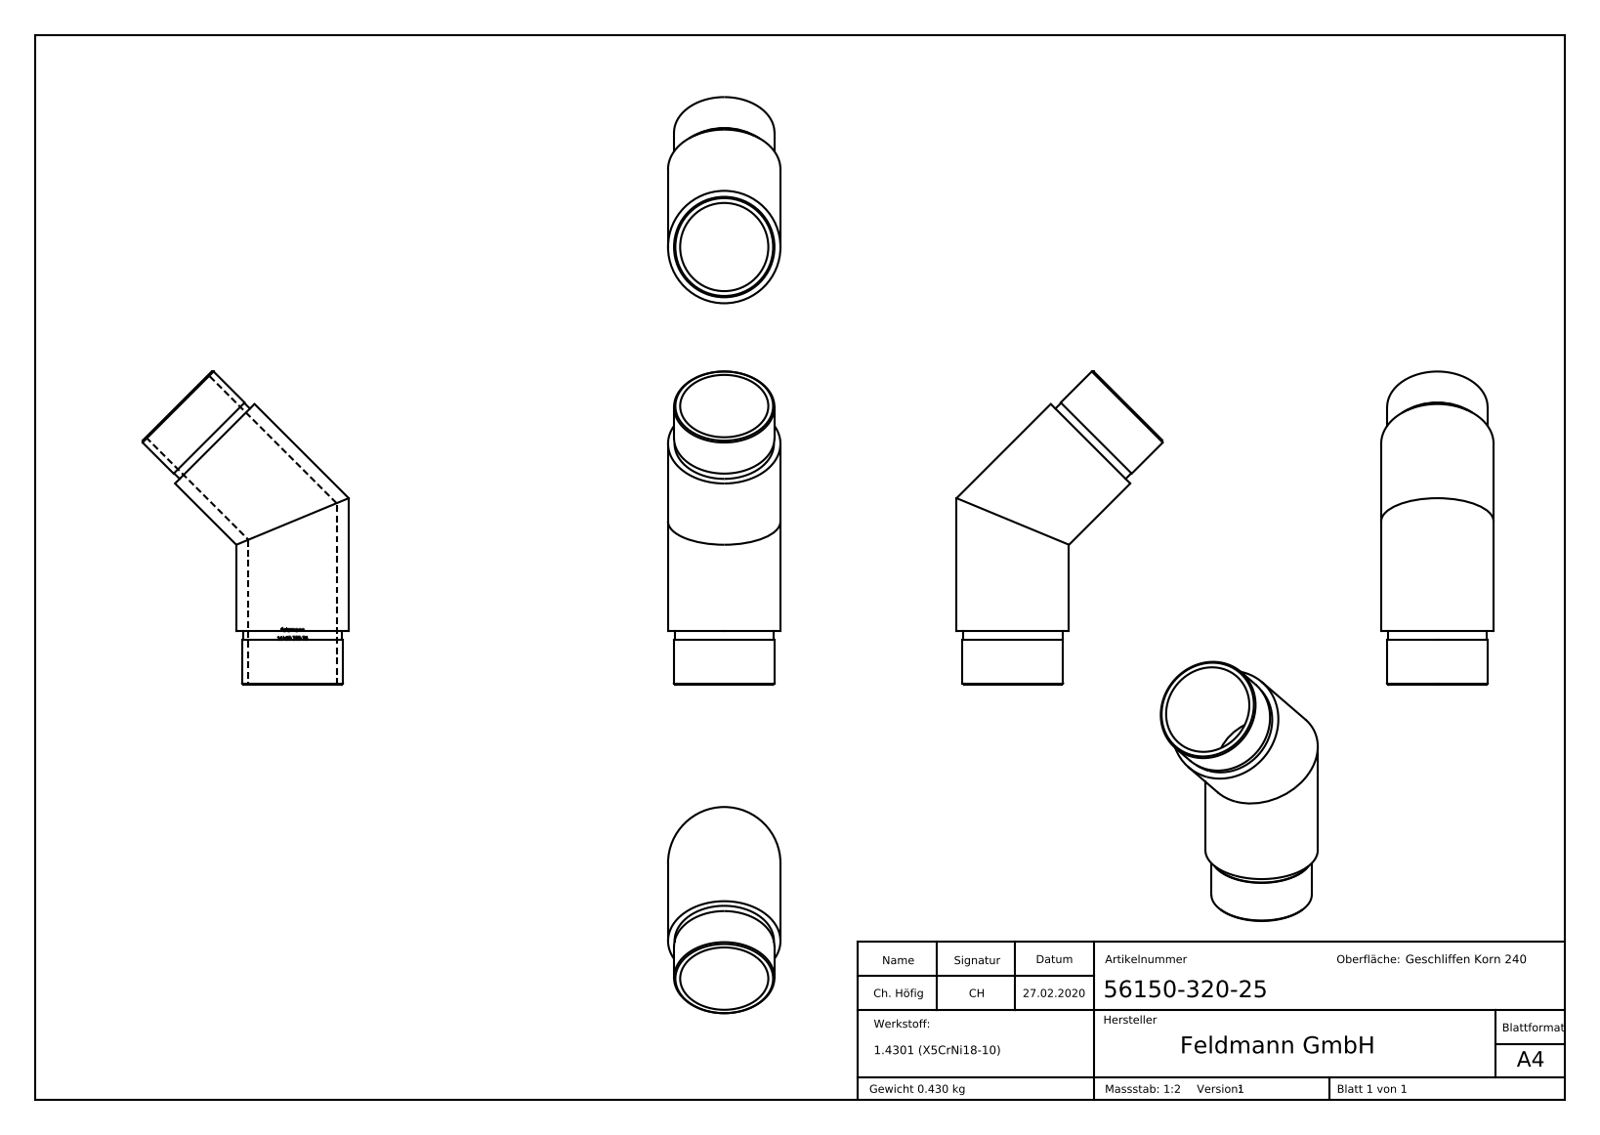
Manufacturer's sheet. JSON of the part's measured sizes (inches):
{"part_name": "56150-320-25", "step_written_by": "SolidWorks 2015 (CONFIG_CONTROL_DESIGN)", "units": "inches", "bodies": {"solids": 1, "faces": 271, "planar": 110, "cylindrical": 34, "other": 127}, "overall_size": [4.628, 3.047, 1.661], "volume_in3": 3.324, "surface_area_in2": 45.76, "round_holes": [[1.303, 2]], "round_bosses_or_shafts": [[1.661, 2], [1.484, 2], [1.469, 2]], "partial_cylinders_radius": [[0.656, 1]], "face_to_face_distances": [0.787, 0.118, 0.669, 0.044, 0.052, 0.047, 0.117, 0.015, 0.08, 0.126]}
